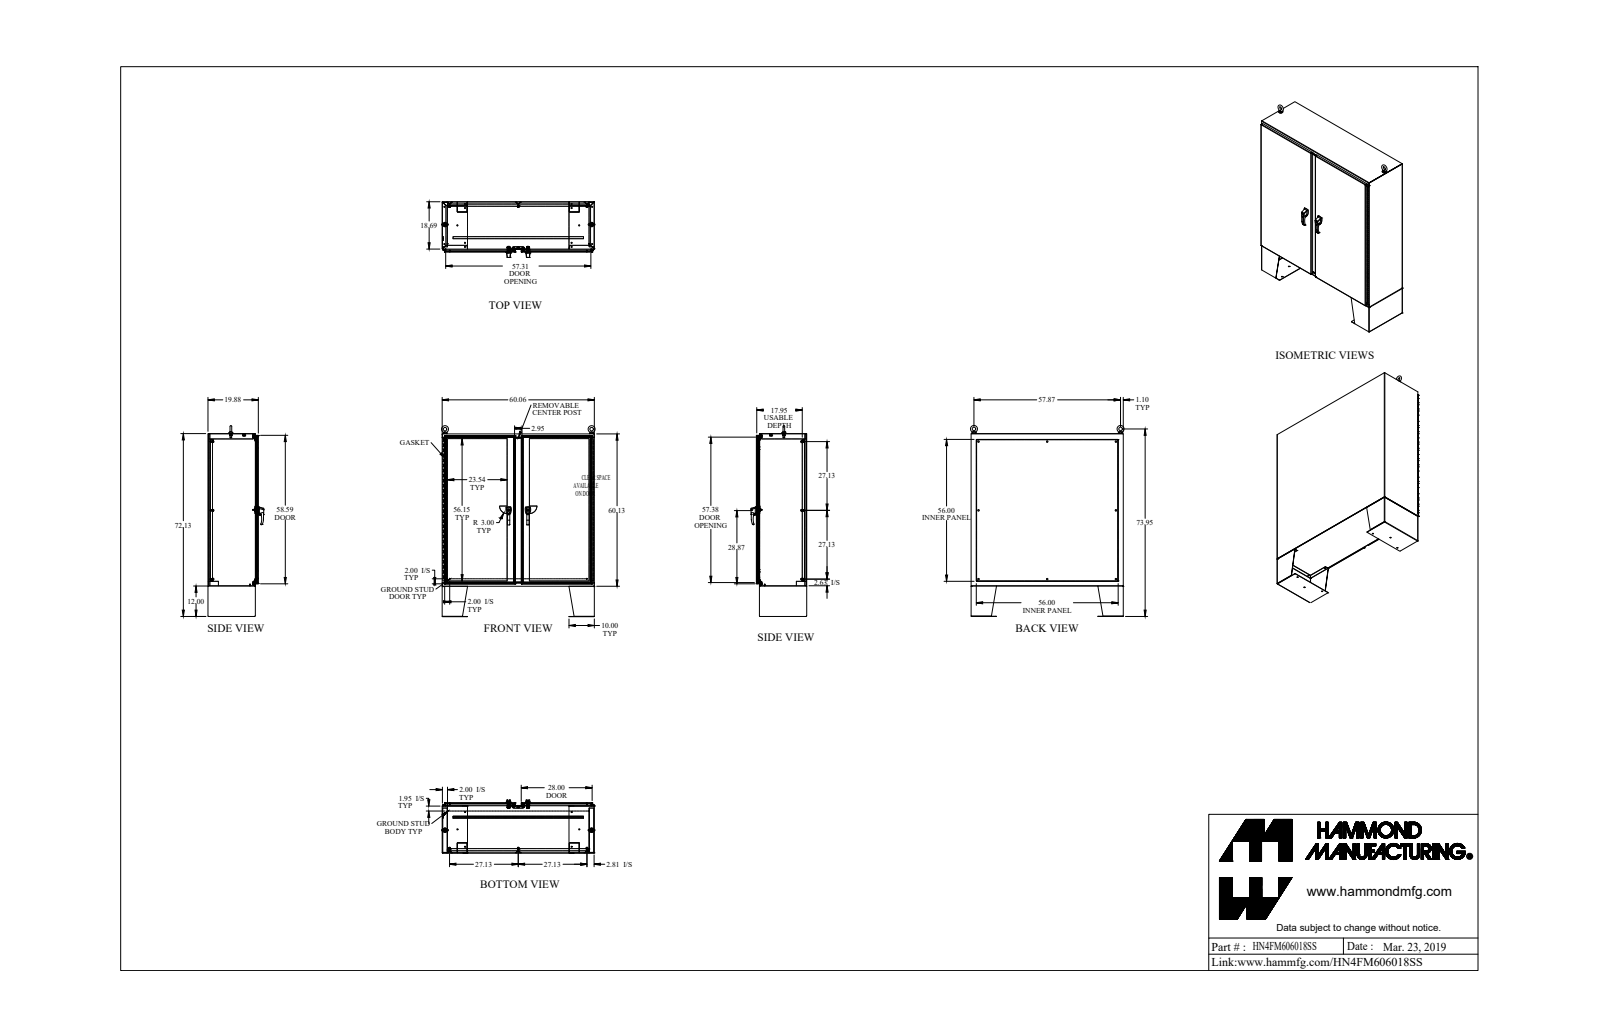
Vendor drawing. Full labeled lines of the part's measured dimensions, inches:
Part name (STEP PRODUCT): HN4FM606018SS
STEP written by: SolidWorks 2018 (AUTOMOTIVE_DESIGN)
Units: inches
Bodies: 130 solids, 3752 faces (1732 planar, 1659 cylindrical, 361 other)
Overall size (bounding box): 75.321 × 60.607 × 21.99
Volume: 1 931 in³ · Surface area: 38 778 in²
Round holes (diameter × count): ⌀0.304 ×20, ⌀0.437 ×14, ⌀0.307 ×8, ⌀0.35 ×8, ⌀0.563 ×8, ⌀0.445 ×7, ⌀0.25 ×6, ⌀0.281 ×4, ⌀0.313 ×4, ⌀0.39 ×4, ⌀0.201 ×3, ⌀0.313 ×3
Round bosses / shafts (diameter × count): ⌀1 ×10, ⌀0.65 ×8, ⌀0.375 ×8, ⌀0.332 ×8, ⌀0.75 ×4, ⌀0.625 ×4, ⌀0.44 ×4, ⌀0.37 ×4
Partial cylindrical surfaces — rounded edges, fillets, slot ends (radius × count): R0.5 ×33, R0.018 ×32, R0.125 ×32, R0.06 ×28, R0.048 ×27, R0.143 ×27, R0.03 ×12, R0.09 ×12
Main face-to-face distances: 0.095, 19.78, 19.685, 0.125, 17.998, 19.875, 1.782, 1.687, 18.093, 1.657
Hole centre spacings: 6, 12, 18, 24, 54.25, 30, 58.513, 1.61
